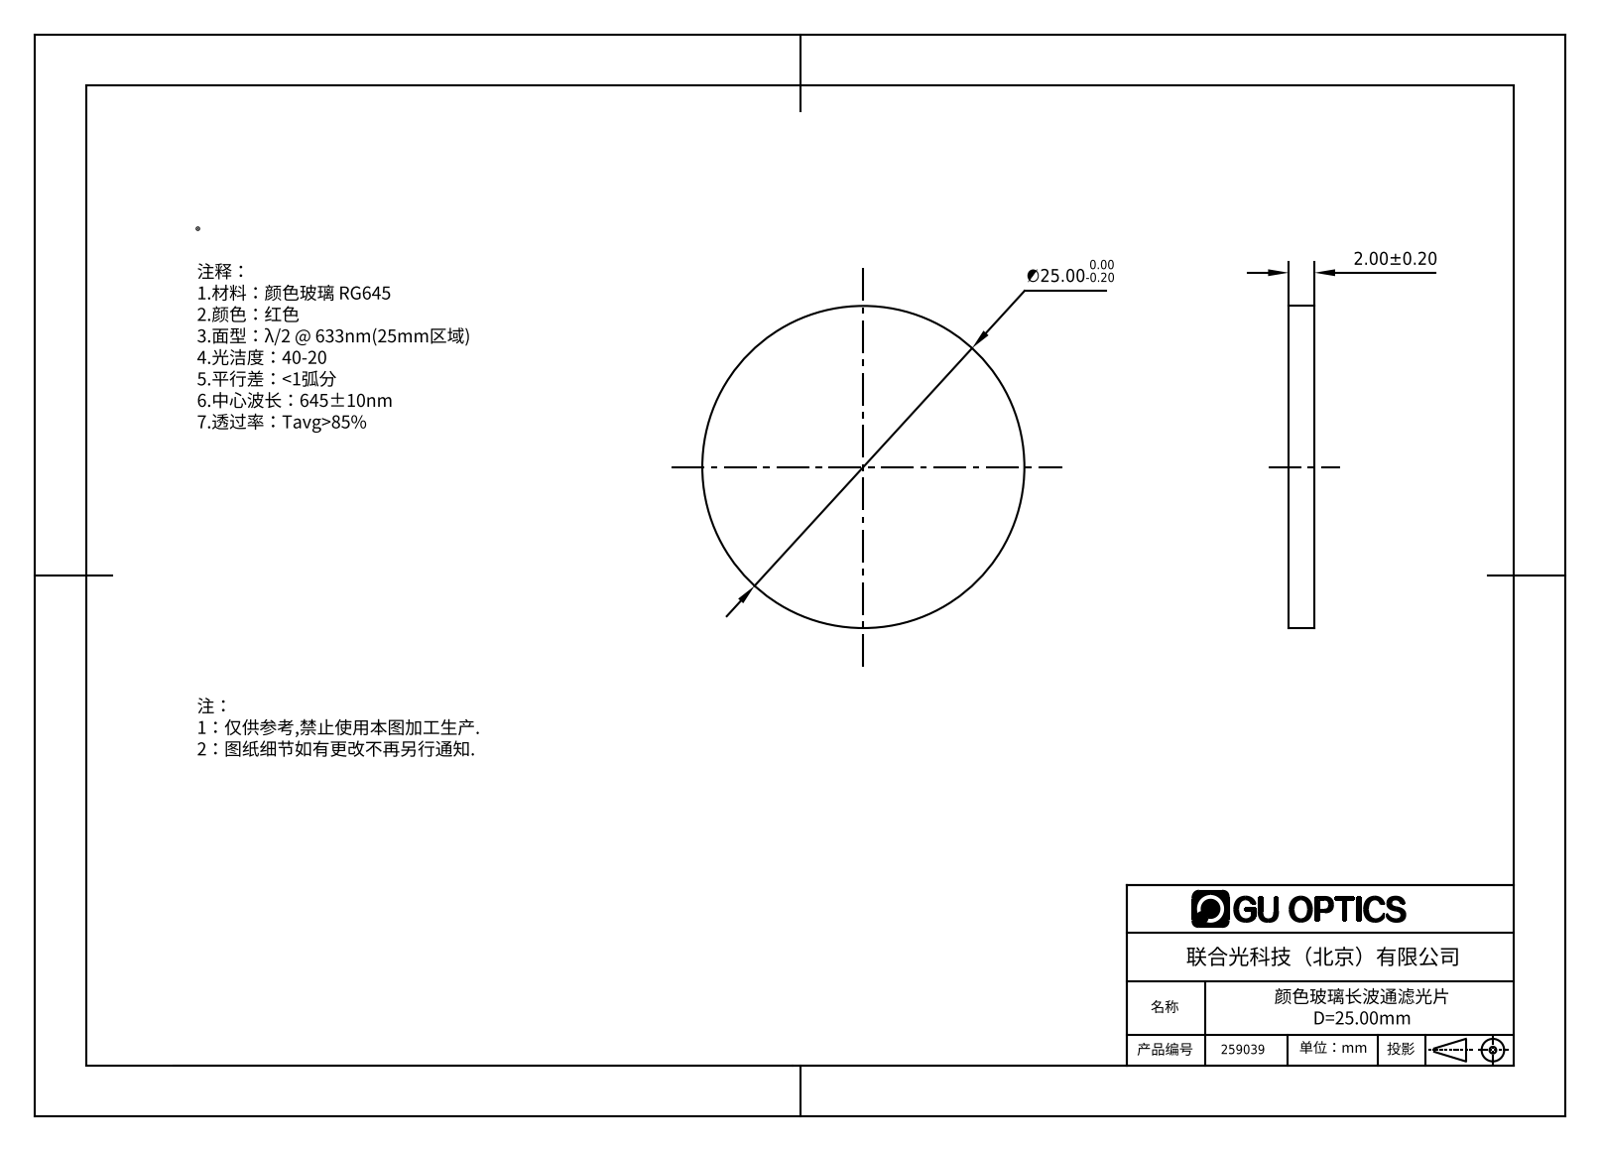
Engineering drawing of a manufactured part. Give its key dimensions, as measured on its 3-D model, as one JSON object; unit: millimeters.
{"part_name": "258511", "step_written_by": "SolidWorks 2016 (AUTOMOTIVE_DESIGN)", "units": "millimeters", "bodies": {"solids": 1, "faces": 4, "planar": 2, "cylindrical": 2, "other": 0}, "overall_size": [25, 25, 2], "volume_mm3": 982, "surface_area_mm2": 1139, "round_bosses_or_shafts": [[25, 1]], "face_to_face_distances": [2]}
